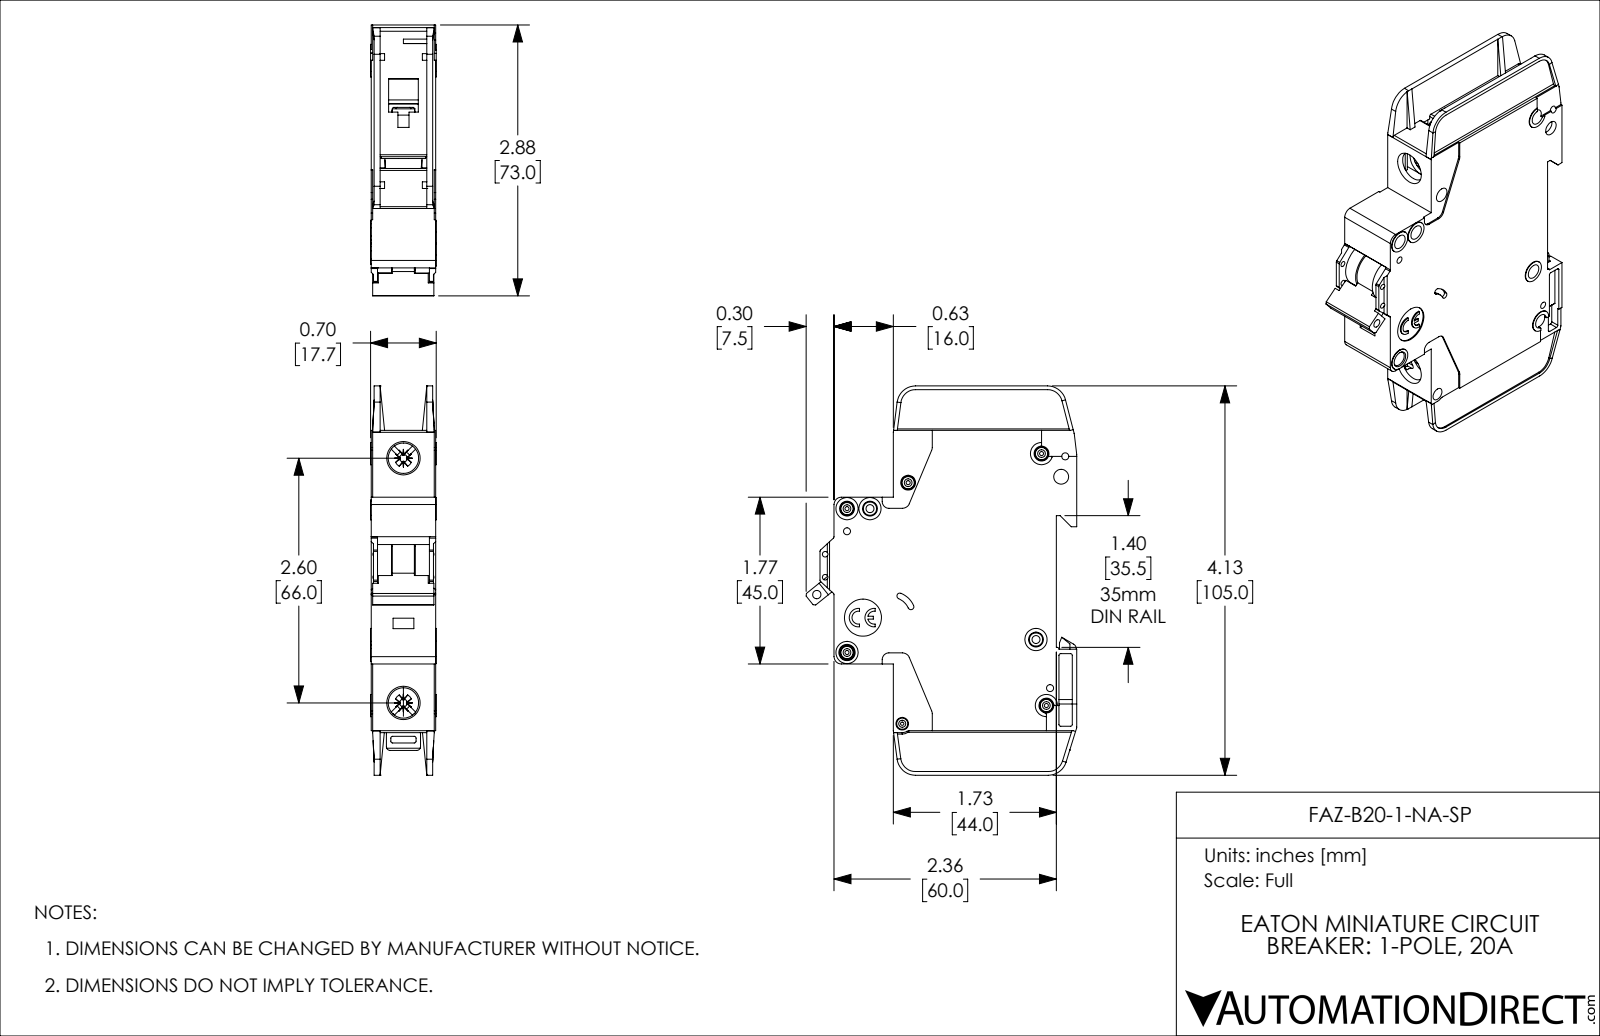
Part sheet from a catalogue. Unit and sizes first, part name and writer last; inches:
Units: inches
Overall size (bounding box): 4.134 × 2.876 × 0.697
Round holes (diameter × count): ⌀0.157 ×8, ⌀0.043 ×5, ⌀0.075 ×4, ⌀0.059 ×2, ⌀0.085 ×2, ⌀0.323 ×2, ⌀0.035 ×1, ⌀0.089 ×1, ⌀0.098 ×1, ⌀0.134 ×1, ⌀0.394 ×1
Round bosses / shafts (diameter × count): ⌀0.13 ×5, ⌀0.236 ×4, ⌀0.118 ×2, ⌀0.098 ×1
Partial cylindrical surfaces — rounded edges, fillets, slot ends (radius × count): R0.02 ×42, R0.016 ×10, R0.039 ×10, R0.079 ×8, R0.197 ×5, R0.008 ×4, R0.026 ×4, R0.043 ×4
Main face-to-face distances: 0.047, 0.685, 0.591, 0.638, 0.094, 0.543, 0.016, 0.031, 0.496, 0.575
Hole centre spacings: 0.244, 0.537, 0.87, 0.189, 0.199, 0.204, 0.221, 0.24
Volume: 4.682 in³ · Surface area: 41.01 in²
Bodies: 1 solid, 1127 faces (671 planar, 357 cylindrical, 99 other)
Part name (STEP PRODUCT): FAZ-B20-1-NA-SP
STEP written by: SolidWorks 2019 (AUTOMOTIVE_DESIGN)
